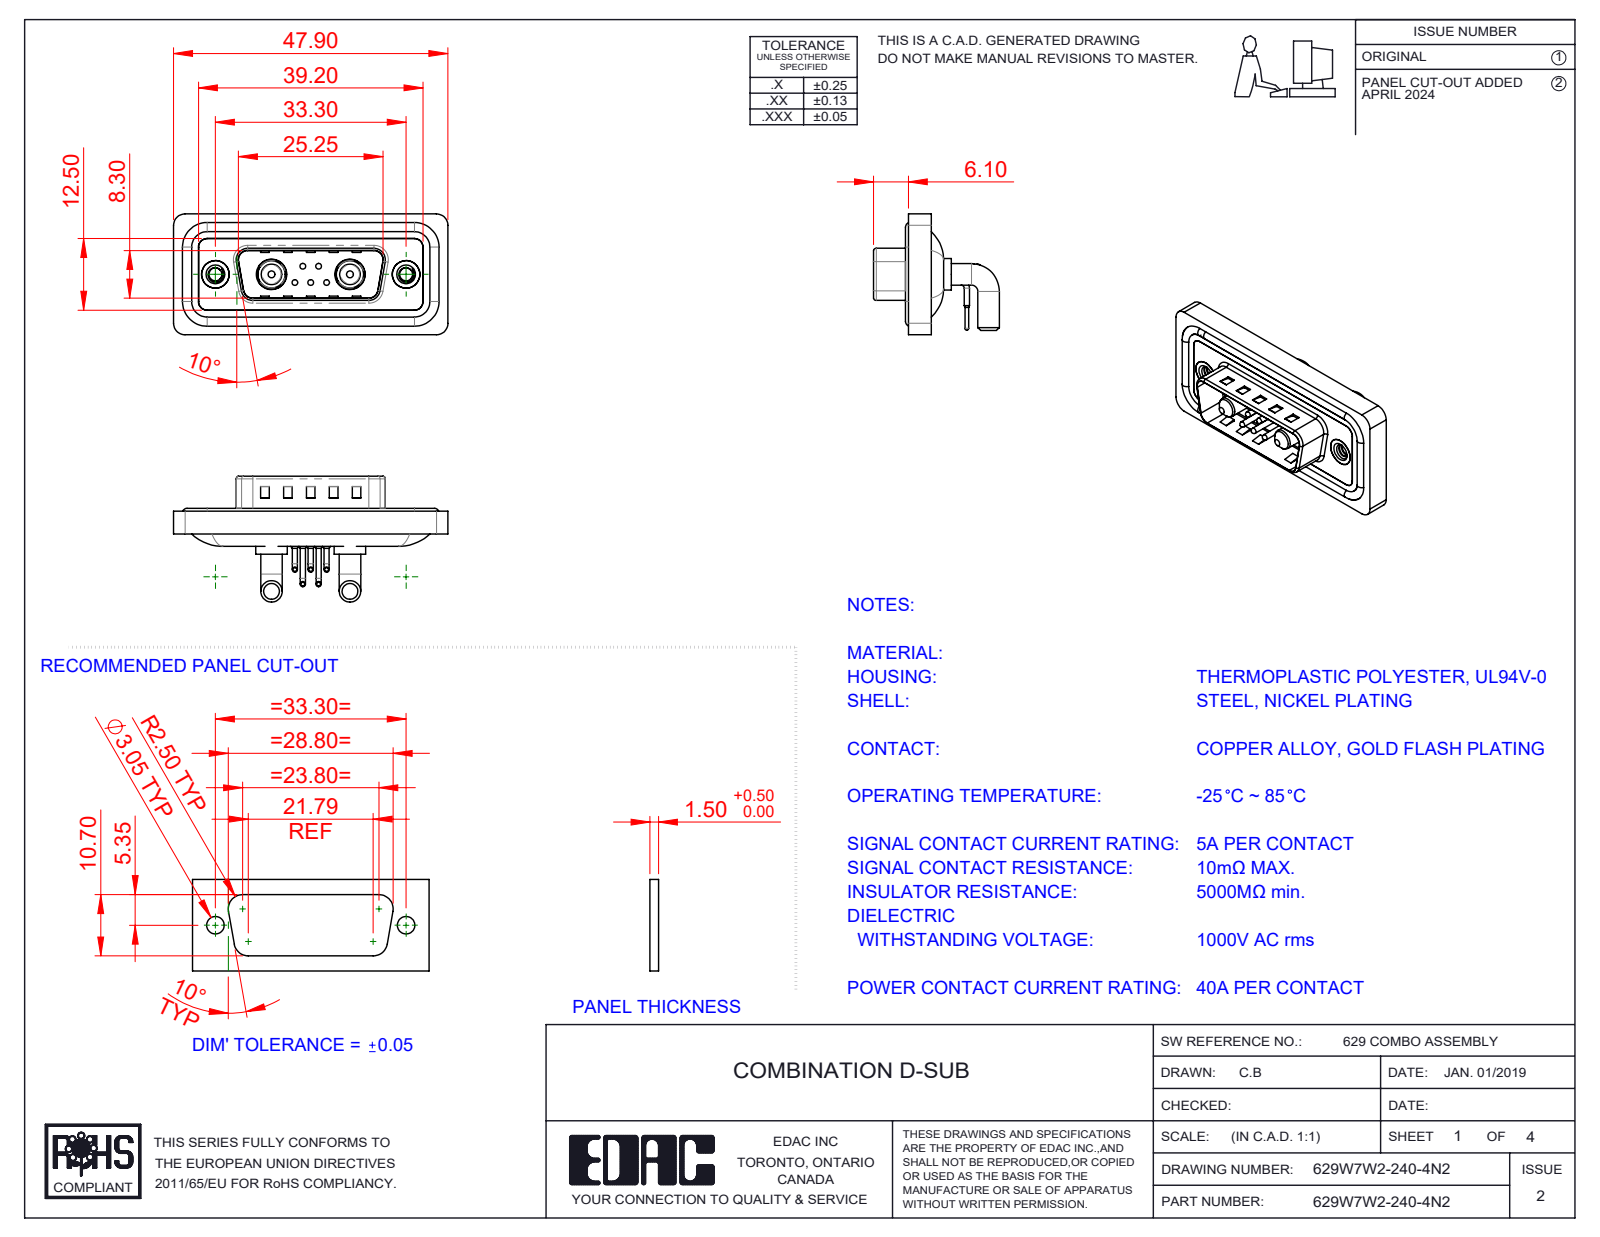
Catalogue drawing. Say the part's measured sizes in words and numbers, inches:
The part is named "629Combo Threaded Rivet_2; 629Combo Contact Row 1; 629Combo Shell Rear_15 Contacts; 629Combo Contact Row 2 (+5 more)". Its 3-D file was written by "SolidWorks 2023 (CONFIG_CONTROL_DESIGN)". It is 16 solids with 1083 faces: 517 planar, 406 cylindrical and 160 other. Overall it measures 1.886 by 0.865 by 0.831 inches. Its volume is 0.356 cubic inches and its surface area 14.3 square inches. Round holes: 5 of diameter 0.03, 5 of diameter 0.063, 5 of diameter 0.079, 2 of diameter 0.089, 2 of diameter 0.157, 2 of diameter 0.189, 2 of diameter 0.191, 2 of diameter 0.197, 2 of diameter 0.209. Round bosses or shafts: 10 of diameter 0.035, 5 of diameter 0.059, 5 of diameter 0.039, 5 of diameter 0.026, 4 of diameter 0.148, 4 of diameter 0.063, 2 of diameter 0.217, 2 of diameter 0.205. Partial cylindrical surfaces (rounded edges, fillets, slot ends): 20 of radius 0.079, 18 of radius 0.059, 8 of radius 0.02, 8 of radius 0.063, 5 of radius 0.04, 4 of radius 0.01, 4 of radius 0.024, 4 of radius 0.026. The main face-to-face distances are 0.016, 0.114, 0.031, 0.043, 0.083, 0.063, 0.098, 0.122, 0.177, 0.161. The hole center spacings are 0.124, 0.109, 0.386, 0.925, 0.17, 0.17, 0.198, 0.198.
